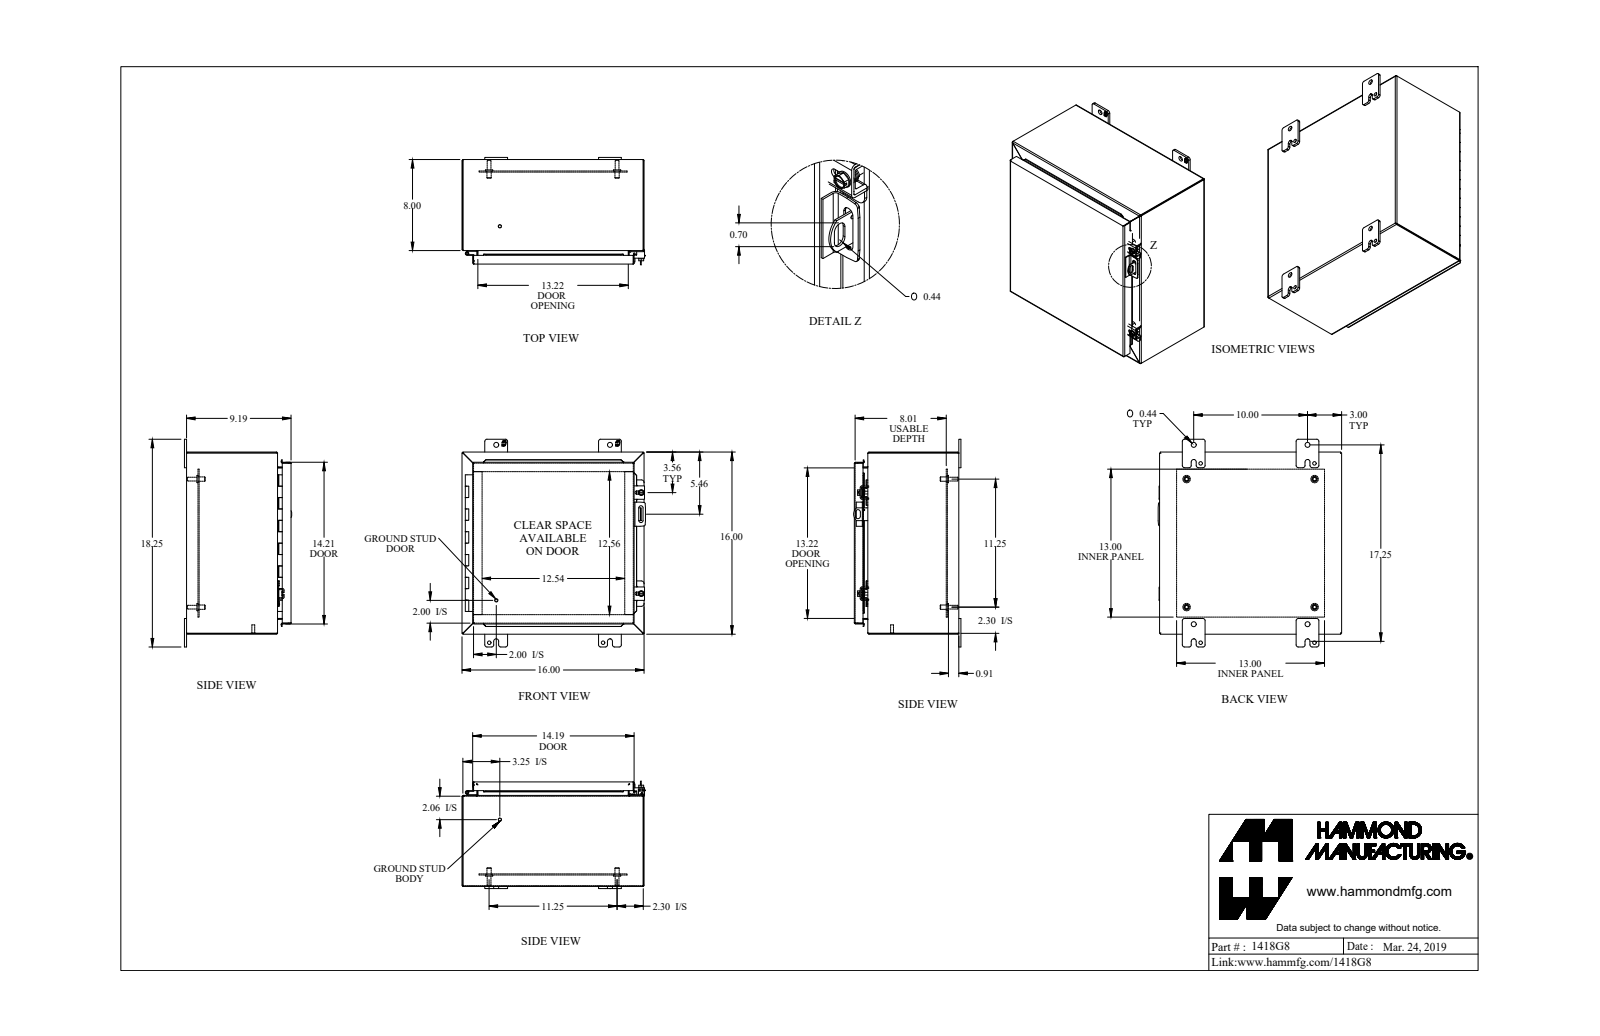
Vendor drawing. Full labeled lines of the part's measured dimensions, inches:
Part name (STEP PRODUCT): 1418G8
STEP written by: SolidWorks 2019 (AUTOMOTIVE_DESIGN)
Units: inches
Bodies: 38 solids, 954 faces (657 planar, 243 cylindrical, 54 other)
Overall size (bounding box): 18.25 × 16.125 × 9.437
Volume: 113.9 in³ · Surface area: 2 964 in²
Round holes (diameter × count): ⌀0.313 ×4, ⌀0.437 ×4, ⌀0.5 ×4, ⌀0.213 ×2, ⌀0.265 ×2, ⌀0.307 ×2, ⌀0.375 ×2, ⌀0.445 ×2, ⌀0.125 ×1, ⌀0.187 ×1
Round bosses / shafts (diameter × count): ⌀0.65 ×4, ⌀0.375 ×4, ⌀0.33 ×4, ⌀1 ×2, ⌀0.5 ×2, ⌀0.39 ×2, ⌀0.281 ×2, ⌀0.25 ×2
Partial cylindrical surfaces — rounded edges, fillets, slot ends (radius × count): R0.188 ×26, R0.036 ×20, R0.108 ×20, R0.048 ×13, R0.143 ×13, R0.007 ×8, R0.045 ×8, R0.079 ×8
Main face-to-face distances: 0.072, 15.928, 9.113, 9.041, 15.856, 16, 9.185, 0.937, 1.009, 0.095
Hole centre spacings: 11.25, 10, 18.656, 1.735, 1.736, 2.434, 3.065, 3.125
